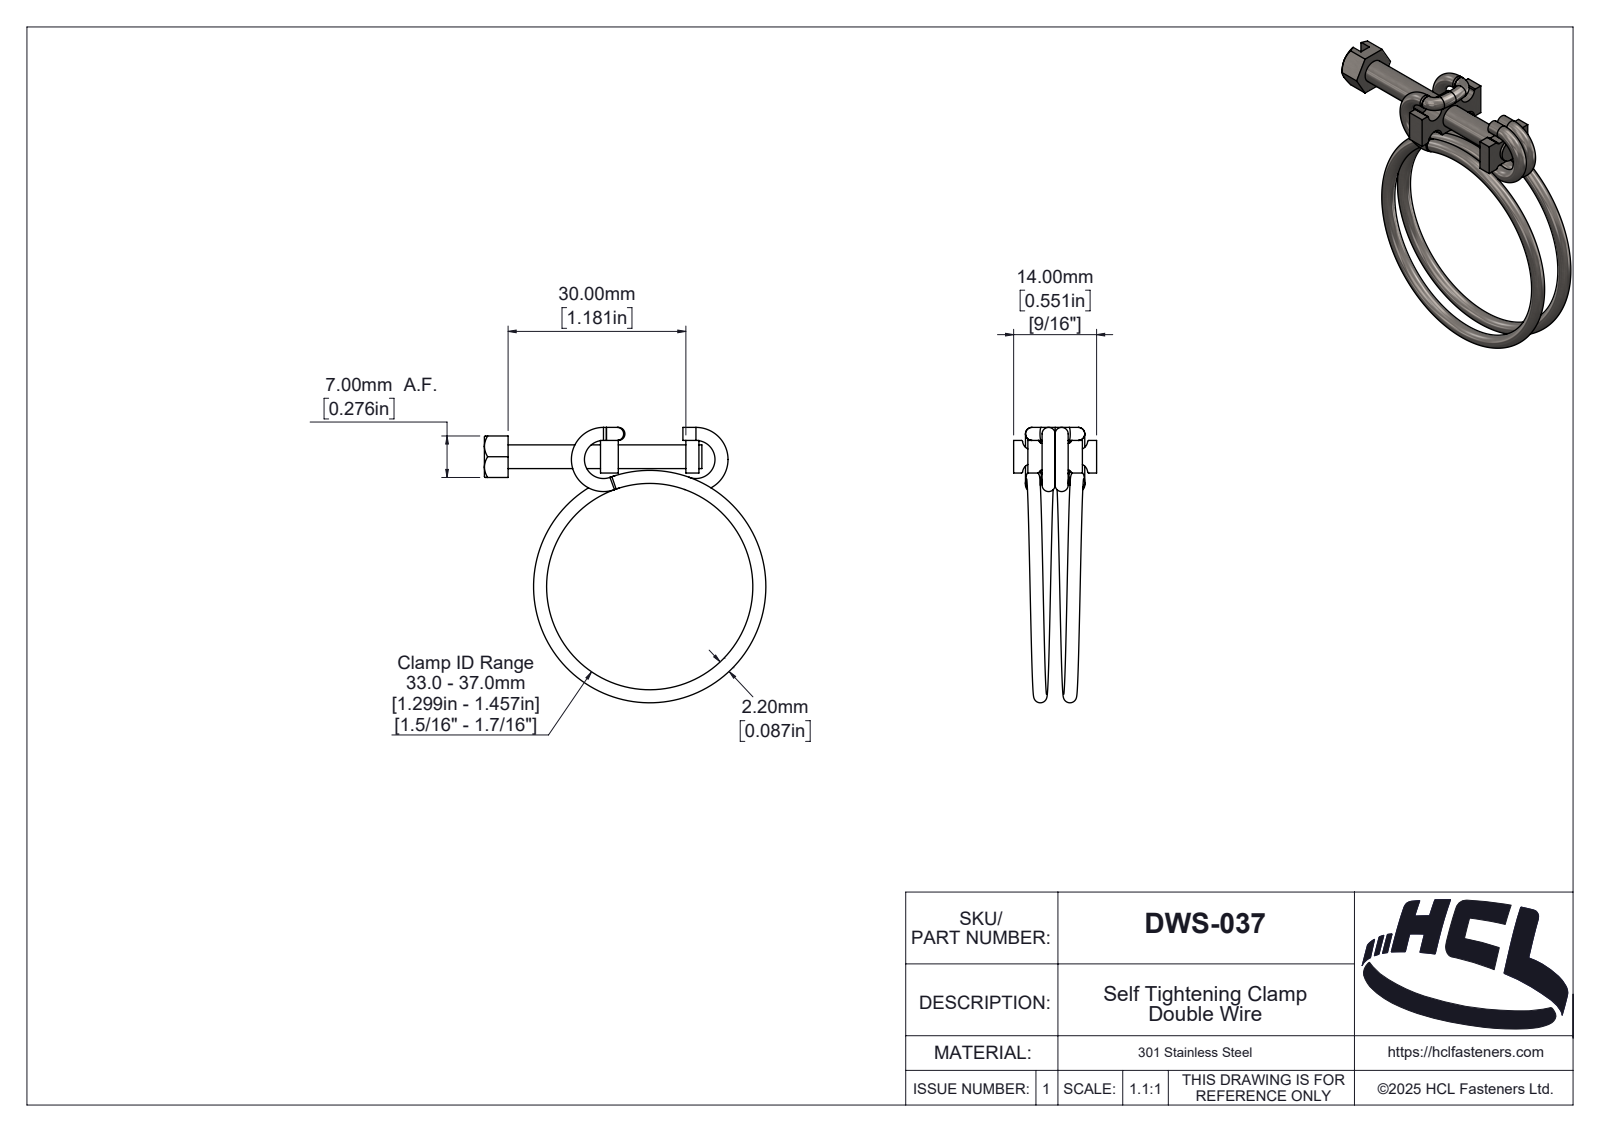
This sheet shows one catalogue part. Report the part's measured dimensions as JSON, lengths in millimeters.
{"part_name": "DWS-037", "step_written_by": "SolidWorks 2025 (AUTOMOTIVE_DESIGN)", "units": "millimeters", "bodies": {"solids": 6, "faces": 209, "planar": 51, "cylindrical": 74, "other": 84}, "overall_size": [47.5, 46.45, 14], "volume_mm3": 2038, "surface_area_mm2": 3372, "round_holes": [[4, 1]], "round_bosses_or_shafts": [[2.2, 4]], "partial_cylinders_radius": [[0.2, 12], [0.5, 4], [1.6, 4], [0.4, 1], [0.51, 1], [0.53, 1], [0.64, 1], [0.91, 1]], "face_to_face_distances": [2, 16.6, 3, 15.6, 18.6, 7, 0.5, 14.4, 11.4, 13.6]}
